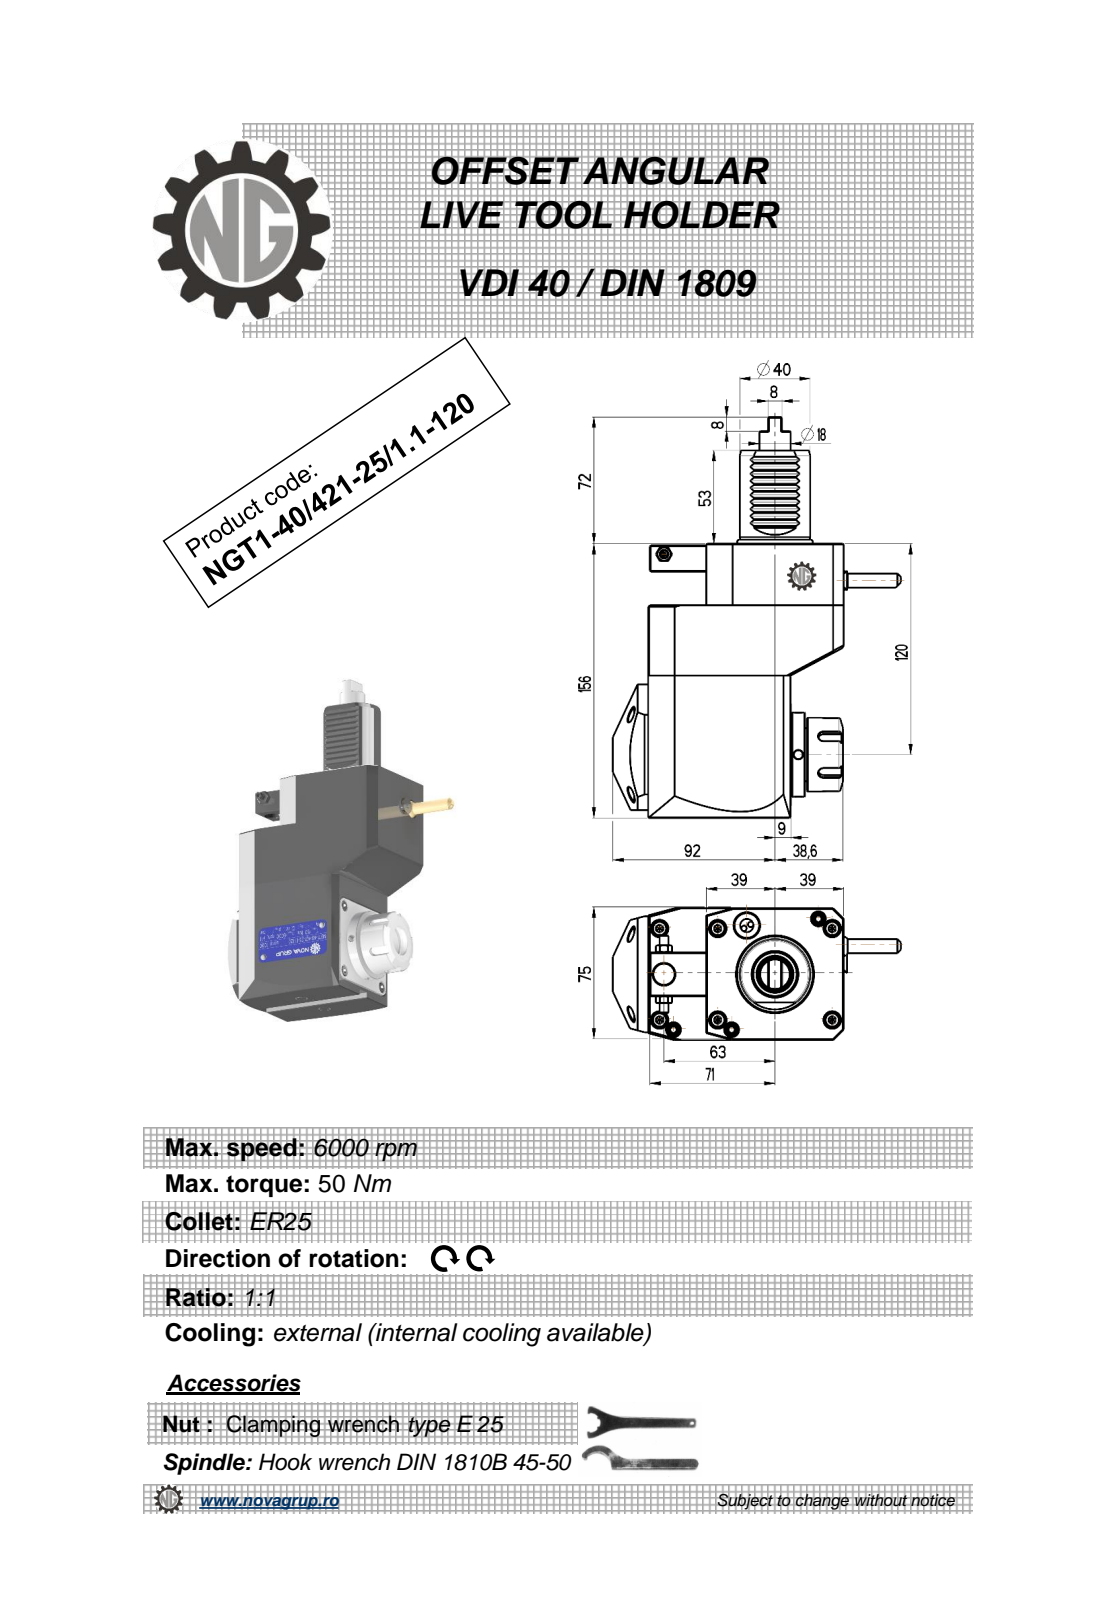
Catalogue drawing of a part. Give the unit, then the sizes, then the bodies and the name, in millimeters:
Units: millimetres
Overall size (bounding box): 228 × 163.5 × 76.6
Round holes (diameter × count): ⌀5 ×3, ⌀3 ×1, ⌀4.2 ×1, ⌀9.5 ×1, ⌀12 ×1, ⌀20.3 ×1
Round bosses / shafts (diameter × count): ⌀48 ×1, ⌀42 ×1, ⌀40 ×1, ⌀38 ×1, ⌀33 ×1, ⌀17.8 ×1, ⌀11.2 ×1, ⌀8.96 ×1
Partial cylindrical surfaces — rounded edges, fillets, slot ends (radius × count): R0.26 ×12, R0.3 ×10, R0.22 ×6, R3 ×5, R0.8 ×2, R0.5 ×1, R40 ×1
Main face-to-face distances: 75, 156, 111, 35, 121, 30, 81, 33, 48, 78
Hole centre spacings: 20.93, 76.25, 100.28, 112.5, 137.15
Volume: 1 166 000 mm³ · Surface area: 86 699 mm²
Bodies: 1 solid, 450 faces (212 planar, 89 cylindrical, 149 other)
Part name (STEP PRODUCT): NGT1_40_421_25_1_1_120
STEP written by: PRO/ENGINEER BY PARAMETRIC TECHNOLOGY CORPORATION, 2010280 (CONFIG_CONTROL_DESIGN)
